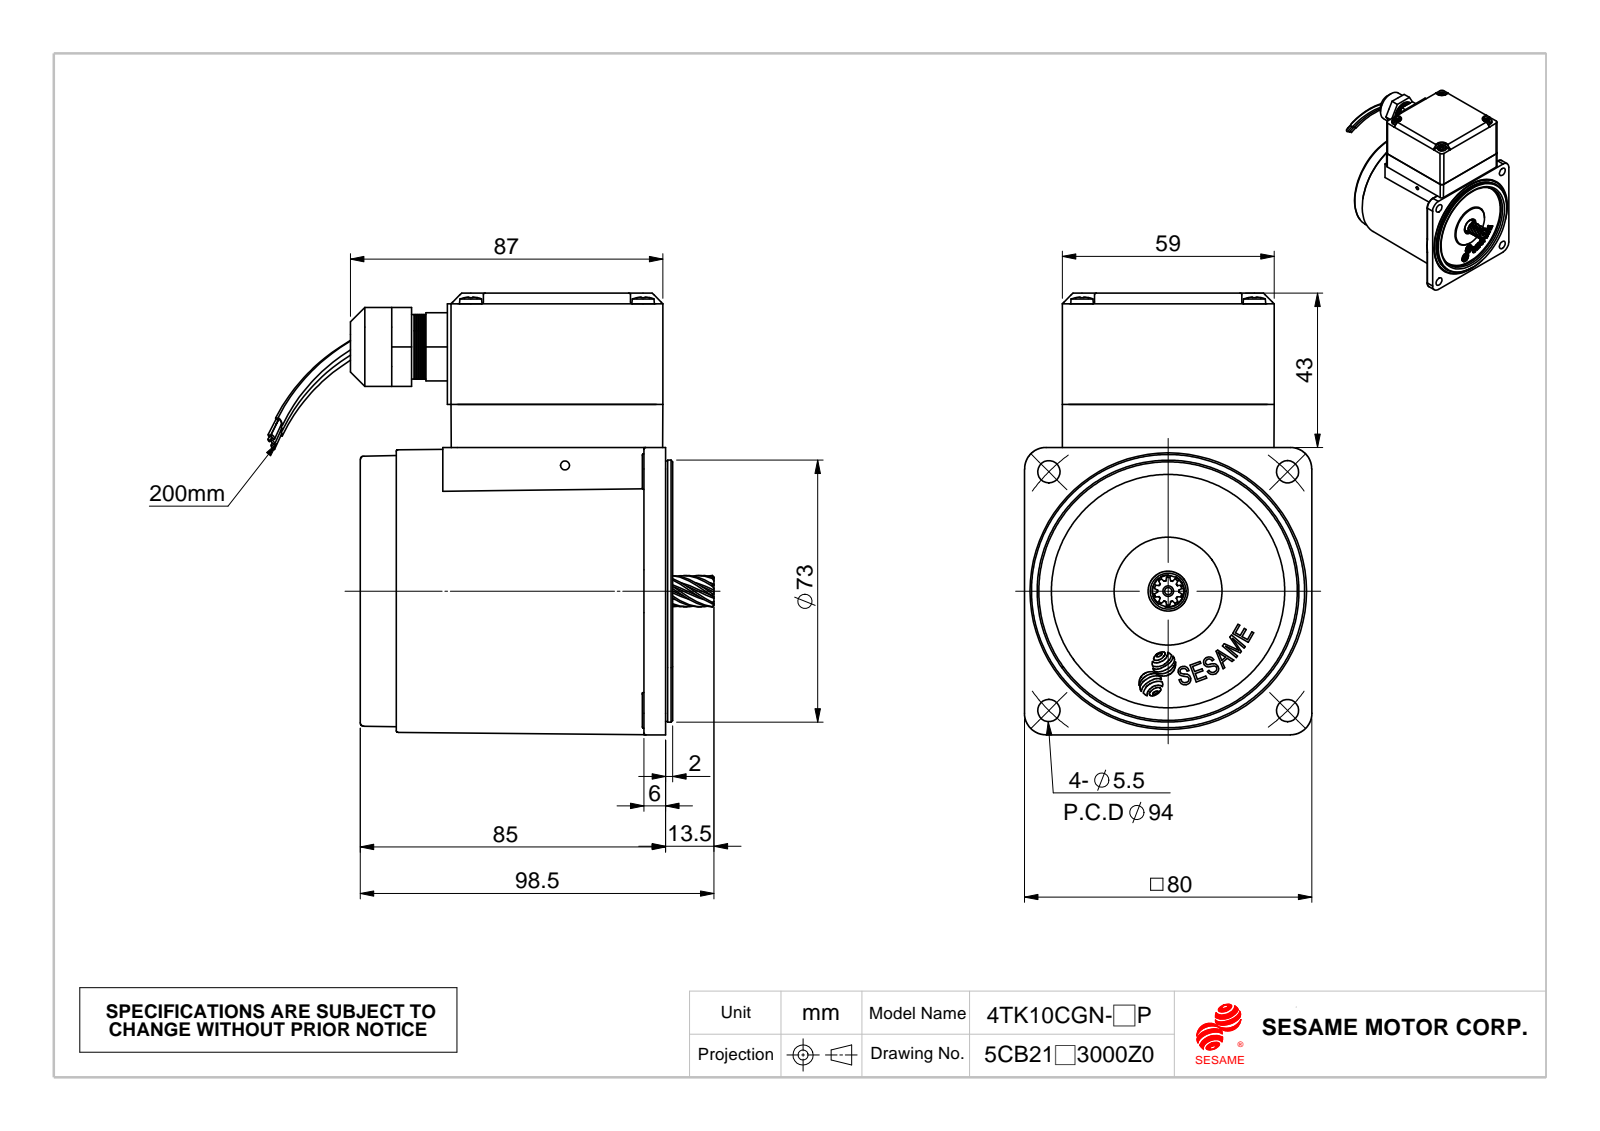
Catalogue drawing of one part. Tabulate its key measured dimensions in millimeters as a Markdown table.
| quantity | value |
| --- | --- |
| part name | Ts下墊片; M425TsA_成品; C475-C473_C475成品-車工; 25GN_Default (+1 more) |
| STEP written by | SolidWorks 2010 (CONFIG_CONTROL_DESIGN) |
| units | millimeters |
| bodies | 14 solids, 2723 faces (295 planar, 941 cylindrical, 1487 other) |
| overall size | 124.22 × 123 × 80 |
| volume | 256 498 mm³ |
| surface area | 102 726 mm² |
| round holes (diameter × count) | 3.3 × 4, 3.5 × 4, 3.9 × 4, 4.3 × 4, 6.2 × 4, 11 × 2, 2 × 1, 2.5 × 1, 12 × 1, 14.5 × 1, 60 × 1, 65 × 1 |
| round bosses / shafts (diameter × count) | 6.3 × 4, 3 × 4, 10 × 2, 72.93 × 1, 72.53 × 1, 37 × 1, 22 × 1, 18 × 1 |
| partial cylindrical surfaces (radius × count) | 0.5 × 12, 2 × 12, 0.61 × 8, 1.16 × 8, 1.29 × 8, 2.26 × 8, 4 × 6, 0.16 × 4 |
| main face-to-face distances | 12, 1, 1.5, 0.5, 3, 0.75, 84, 80, 83, 82.5 |
| hole center spacings | 46.99, 48, 66.46, 11.67, 12.35, 12.7, 24.93, 25 |
